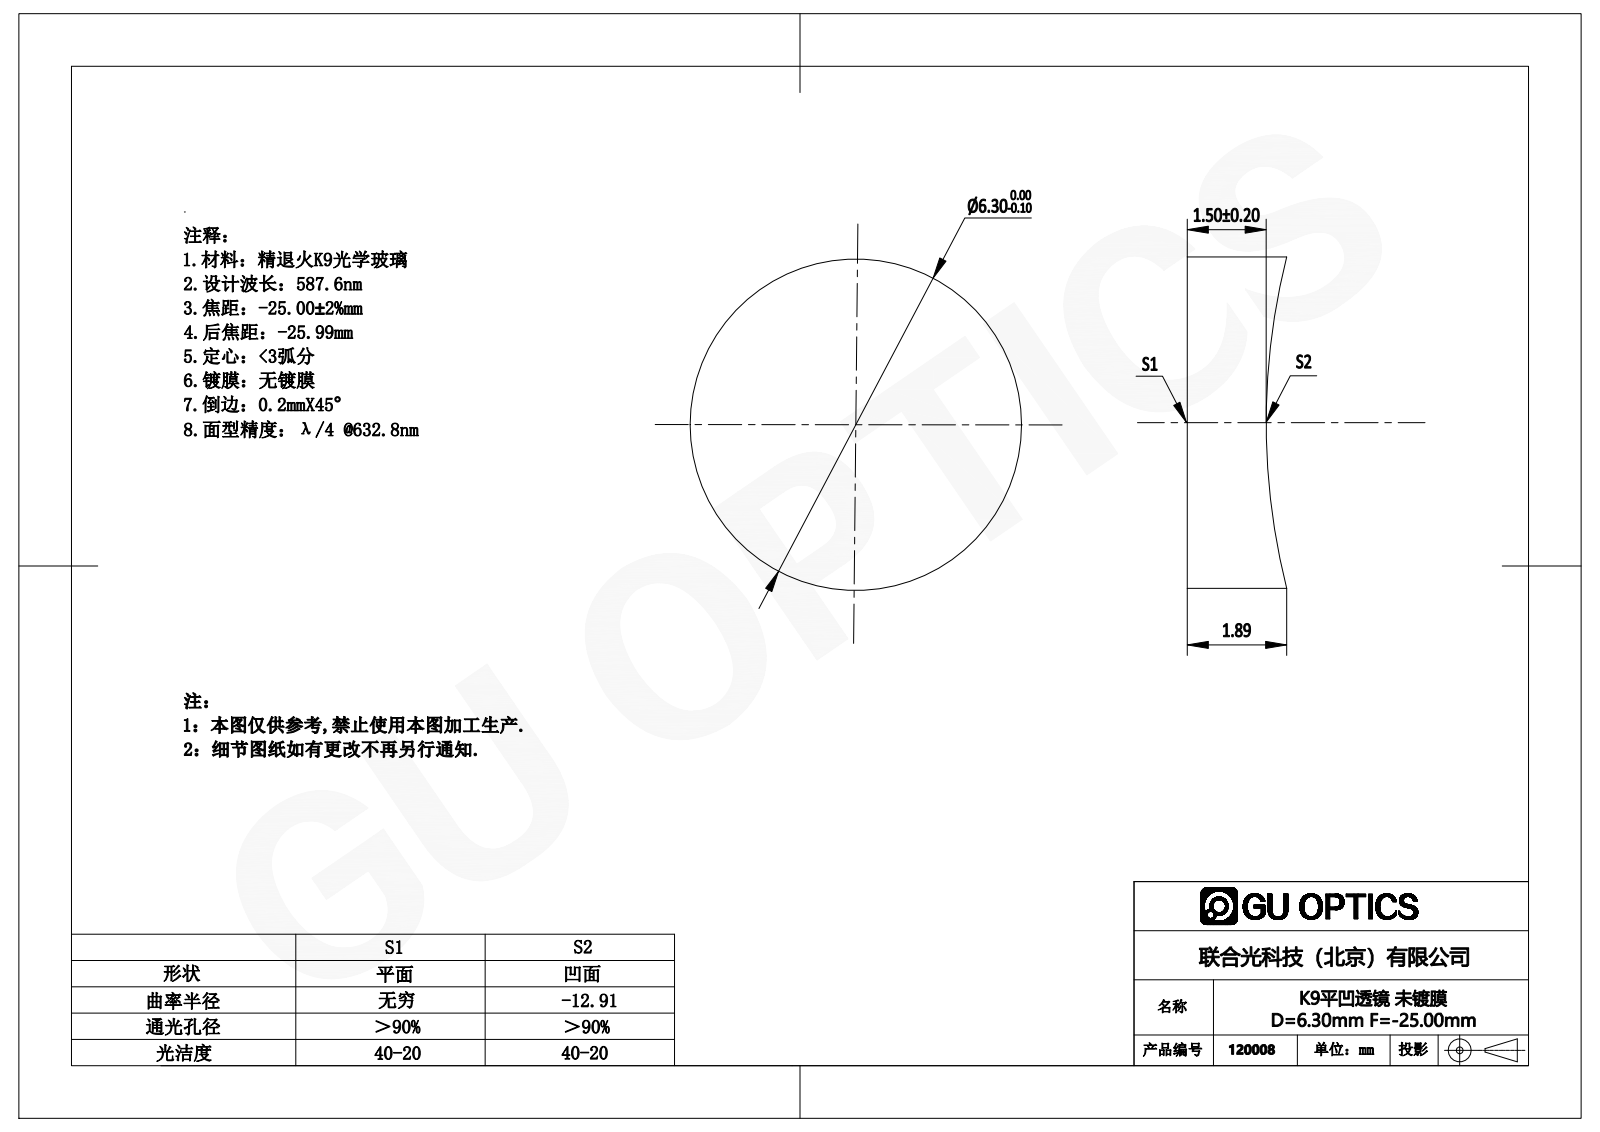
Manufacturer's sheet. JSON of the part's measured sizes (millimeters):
{"part_name": "120008", "step_written_by": "SolidWorks 2016 (AUTOMOTIVE_DESIGN)", "units": "millimeters", "bodies": {"solids": 1, "faces": 5, "planar": 1, "cylindrical": 2, "other": 2}, "overall_size": [6.3, 6.3, 1.89], "volume_mm3": 53, "surface_area_mm2": 100, "round_bosses_or_shafts": [[6.3, 1]]}
